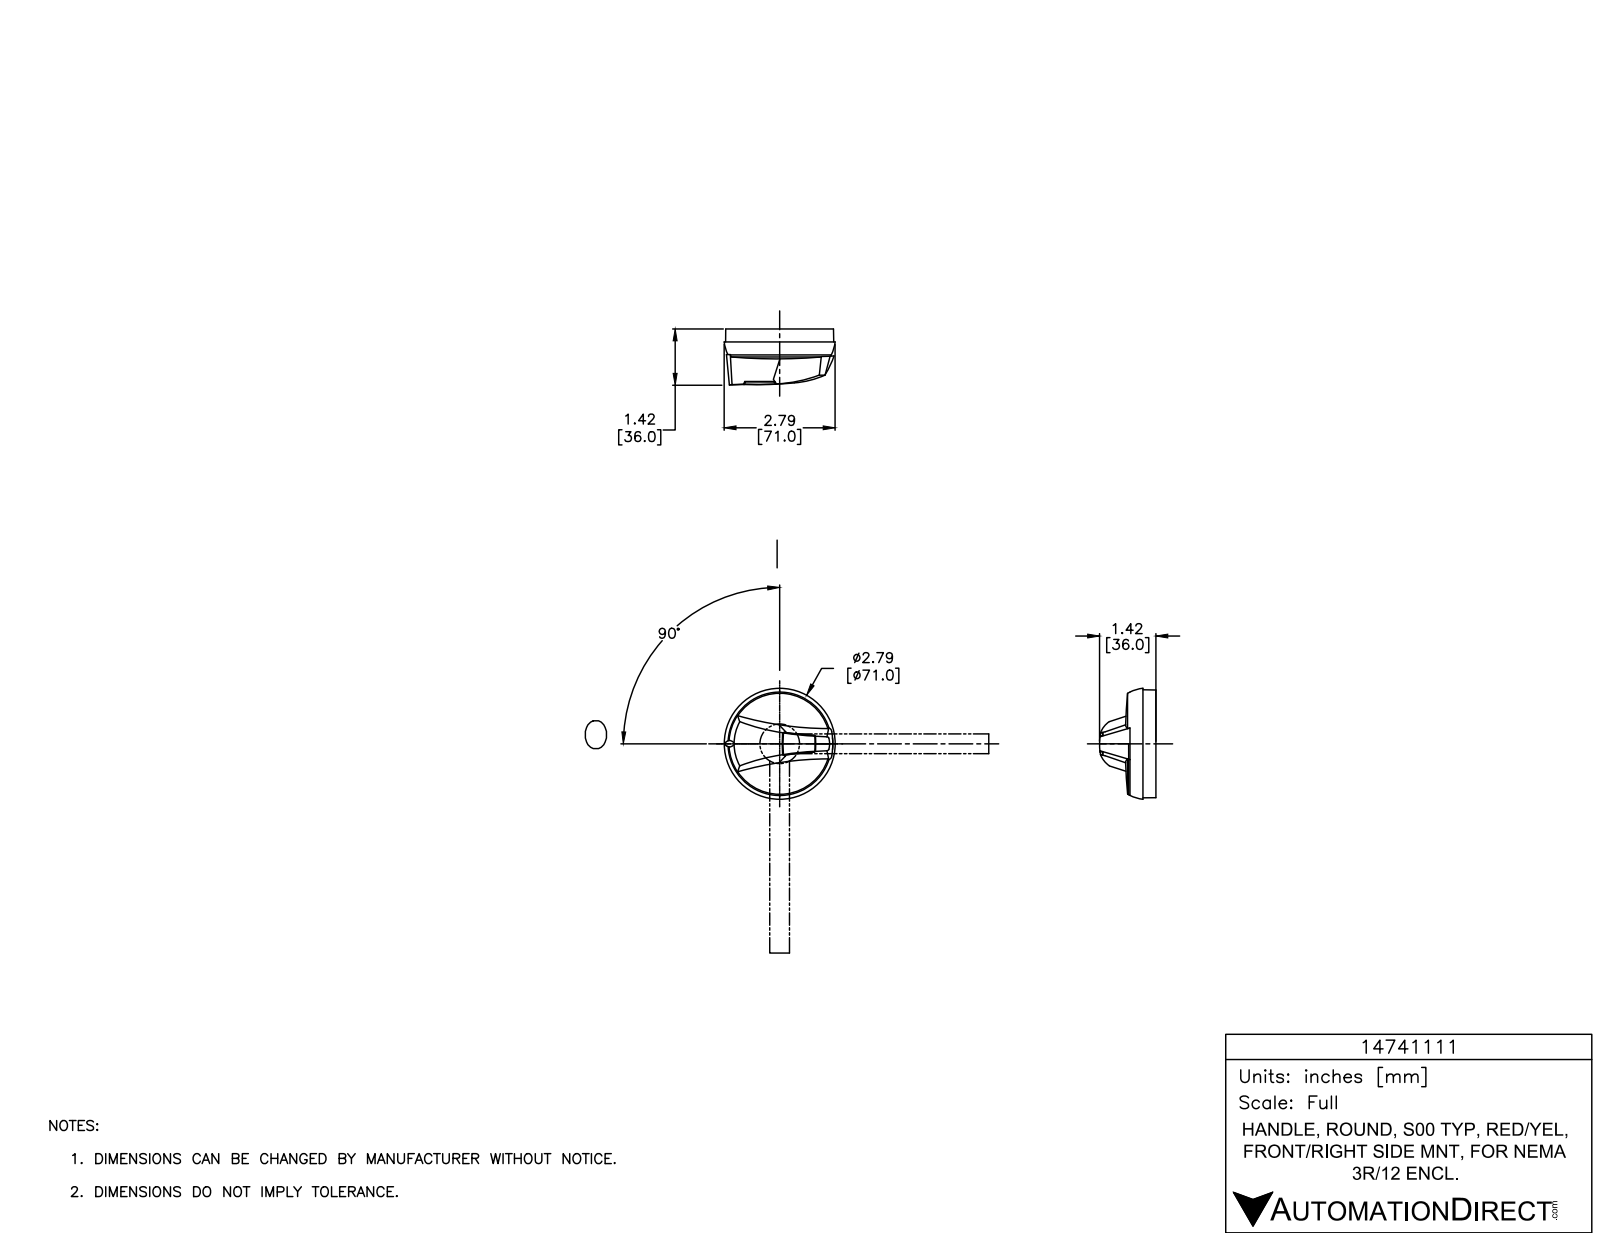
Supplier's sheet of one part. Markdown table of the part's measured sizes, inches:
| quantity | value |
| --- | --- |
| part name | 14741111 |
| STEP written by | SolidWorks 2015 (AUTOMOTIVE_DESIGN) |
| units | inches |
| bodies | 1 solid, 76 faces (29 planar, 14 cylindrical, 33 other) |
| overall size | 2.8 × 2.8 × 1.899 |
| volume | 5.42 in³ |
| surface area | 24.86 in² |
| round holes (diameter × count) | 0.169 × 4, 0.457 × 1, 2.618 × 1 |
| round bosses / shafts (diameter × count) | 0.801 × 1 |
| main face-to-face distances | 0.624, 0.616, 0.03, 0.646, 0.654, 0.488, 0.518, 1.134, 1.142, 0.807 |
| hole center spacings | 0.961, 1.102, 1.575, 1.922 |
